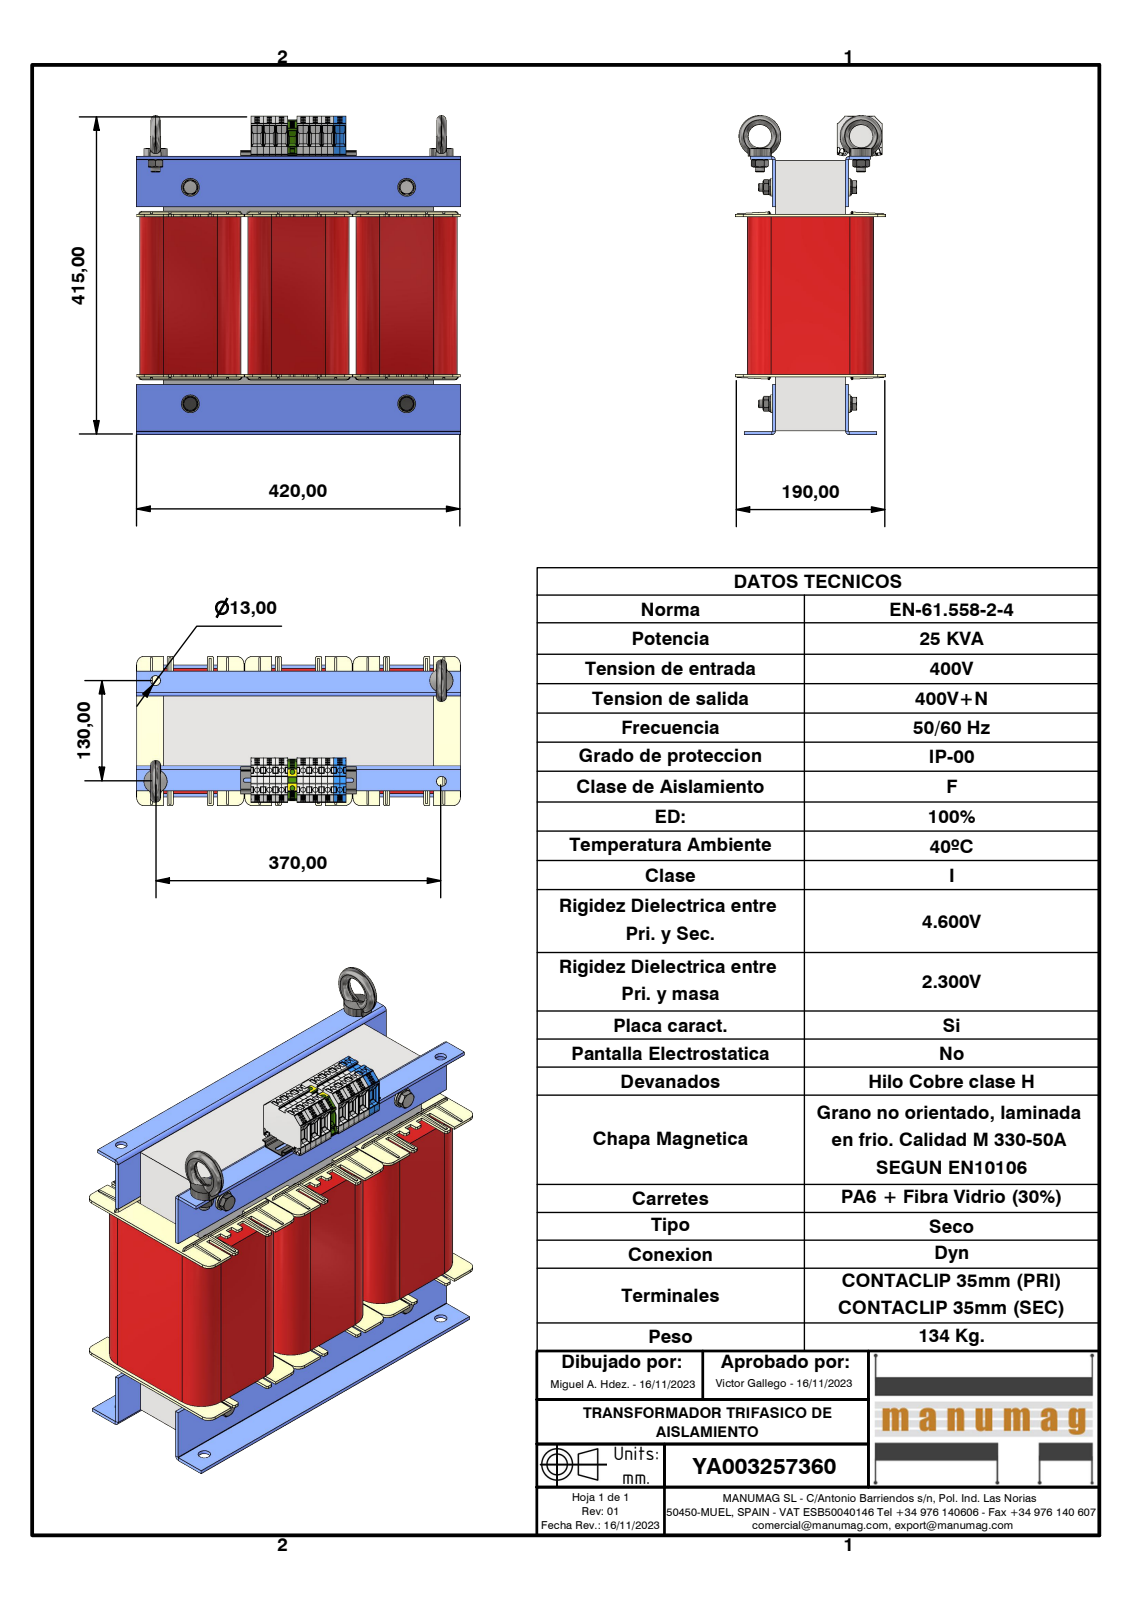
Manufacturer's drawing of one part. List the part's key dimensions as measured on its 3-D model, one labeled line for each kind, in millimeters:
Part name (STEP PRODUCT): YA003257360; 3UI210 350 x 350 - 90; UI 210_90_BOBINADO; RC70 NT071 SUPERIOR (+8 more)
STEP written by: Autodesk Inventor 2023 (AUTOMOTIVE_DESIGN)
Units: millimetres
Bodies: 45 solids, 7122 faces (4104 planar, 2072 cylindrical, 946 other)
Overall size (bounding box): 420 × 413 × 193
Volume: 17 570 000 mm³ · Surface area: 2 130 000 mm²
Round holes (diameter × count): ⌀6.5 ×14, ⌀13 ×6, ⌀15 ×6, ⌀2 ×4, ⌀8.38 ×4, ⌀10 ×4, ⌀10.5 ×4, ⌀14 ×4, ⌀6.3 ×2, ⌀10.11 ×2, ⌀30 ×2
Round bosses / shafts (diameter × count): ⌀23 ×4, ⌀20 ×4, ⌀15.4 ×4, ⌀11.5 ×4, ⌀9.19 ×4, ⌀54 ×2, ⌀12 ×2, ⌀10.8 ×2
Partial cylindrical surfaces — rounded edges, fillets, slot ends (radius × count): R0.3 ×494, R0.5 ×192, R2 ×62, R1 ×42, R0.25 ×34, R5 ×20, R4 ×14, R2.6 ×12
Main face-to-face distances: 140, 70, 2, 280, 210, 27.25, 28.41, 1.16, 4, 30.41
Hole centre spacings: 15.9, 29.63, 25, 31.8, 40.45, 59.6, 64.63, 75.5
